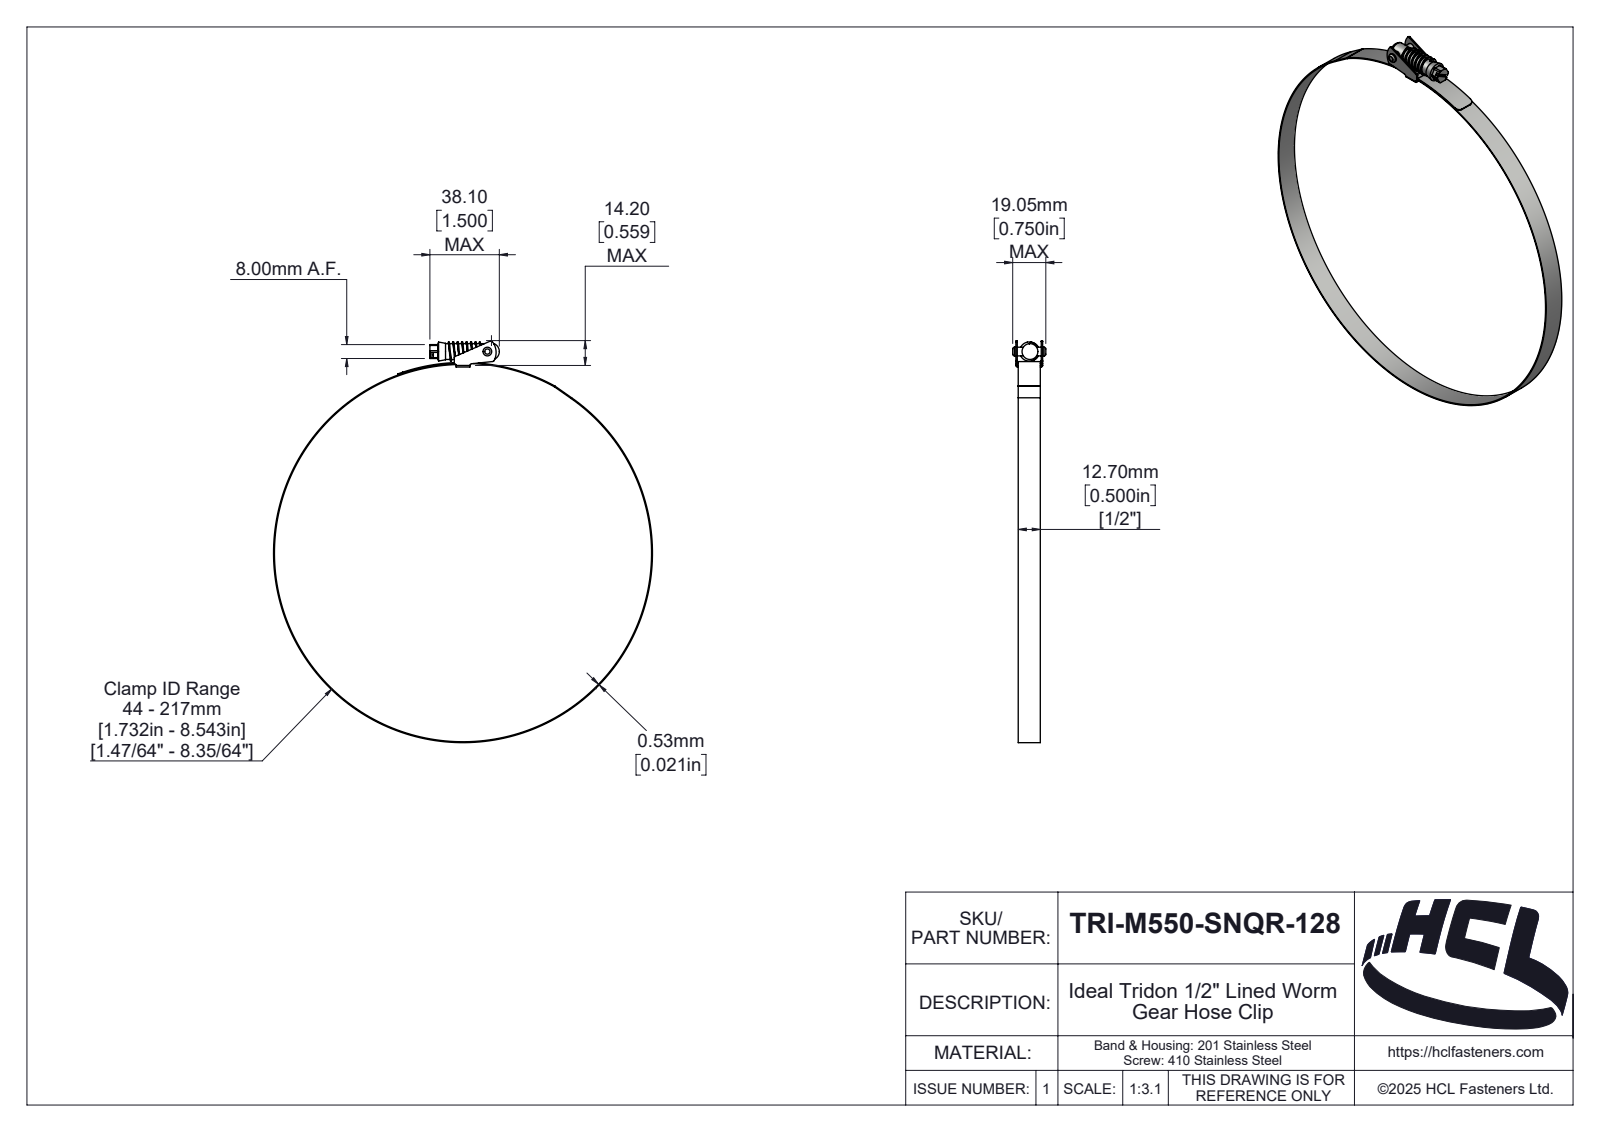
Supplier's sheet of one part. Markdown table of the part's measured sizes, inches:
| quantity | value |
| --- | --- |
| part name | TRI-M550-SNQR-128 |
| STEP written by | SolidWorks 2025 (AUTOMOTIVE_DESIGN) |
| units | inches |
| bodies | 5 solids, 222 faces (44 planar, 112 cylindrical, 66 other) |
| overall size | 9.095 × 8.585 × 0.75 |
| volume | 0.49 in³ |
| surface area | 35.16 in² |
| round holes (diameter × count) | 0.197 × 1, 8.543 × 1 |
| round bosses / shafts (diameter × count) | 8.585 × 1, 0.358 × 1 |
| partial cylindrical surfaces (radius × count) | 0.039 × 11, 0.004 × 2, 0.035 × 2, 0.118 × 2, 0.018 × 1, 0.074 × 1, 0.079 × 1, 0.093 × 1 |
| main face-to-face distances | 0.031, 0.053, 0.553, 0.5, 0.575, 0.022, 0.522, 0.606, 0.543, 0.021 |
| hole center spacings | 4.596 |
